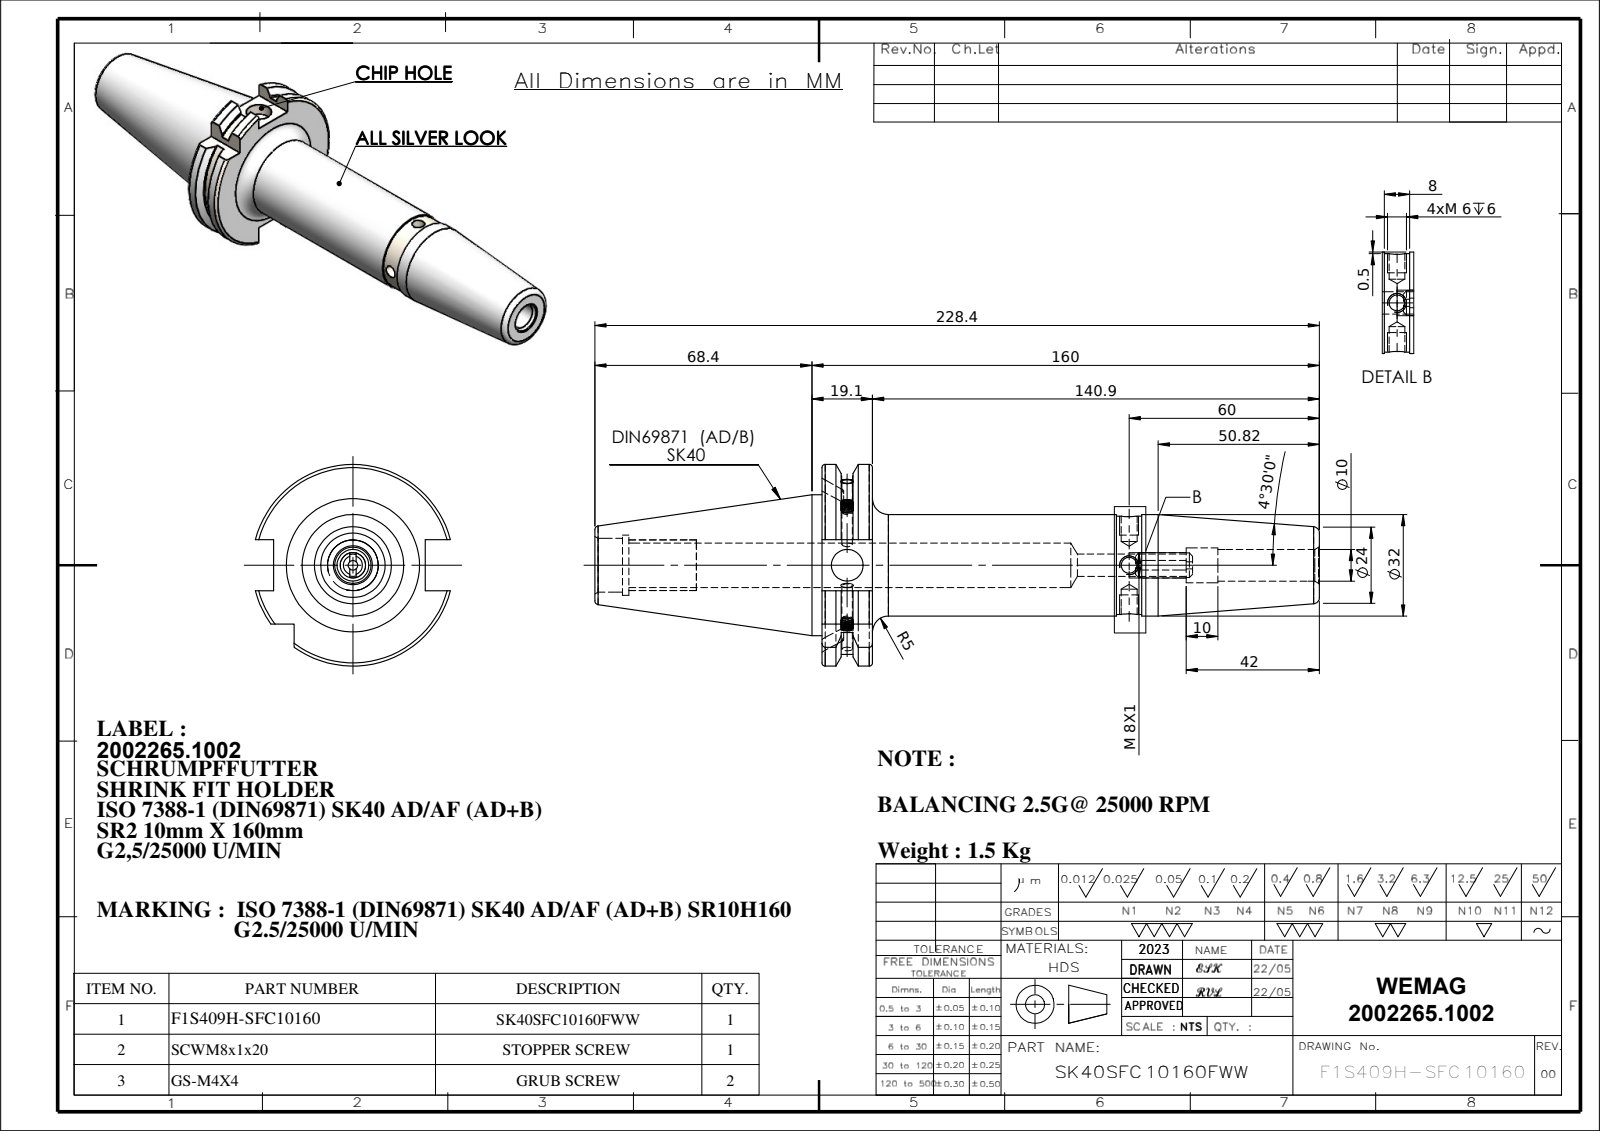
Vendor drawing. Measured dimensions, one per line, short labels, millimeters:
name: GS-M4X4_DIN 913 - M4 x 4-N; SK40SFC10160FWW; SCWM8X20; 91406-SR10160
written by: SolidWorks 2018 (CONFIG_CONTROL_DESIGN)
unit: mm
bodies: 4 solids, 242 faces (66 planar, 70 cylindrical, 106 other)
size: 228.4 × 63.55 × 61.48
volume: 187 899 mm³; area: 40 770 mm²
holes: 2× ⌀5, 1× ⌀3, 1× ⌀3.3, 1× ⌀7, 1× ⌀9.99, 1× ⌀10, 1× ⌀10.99, 1× ⌀14, 1× ⌀17, 1× ⌀19
bosses: 2× ⌀4, 1× ⌀44.45, 1× ⌀32, 1× ⌀31, 1× ⌀8
rounds: 1× R28.12, 1× R31.77
face distances: 15.9, 156.8, 140.9, 16.1, 47.8, 71.6, 87.5, 228.4, 10.7, 60.9
hole spacings: 88.85
